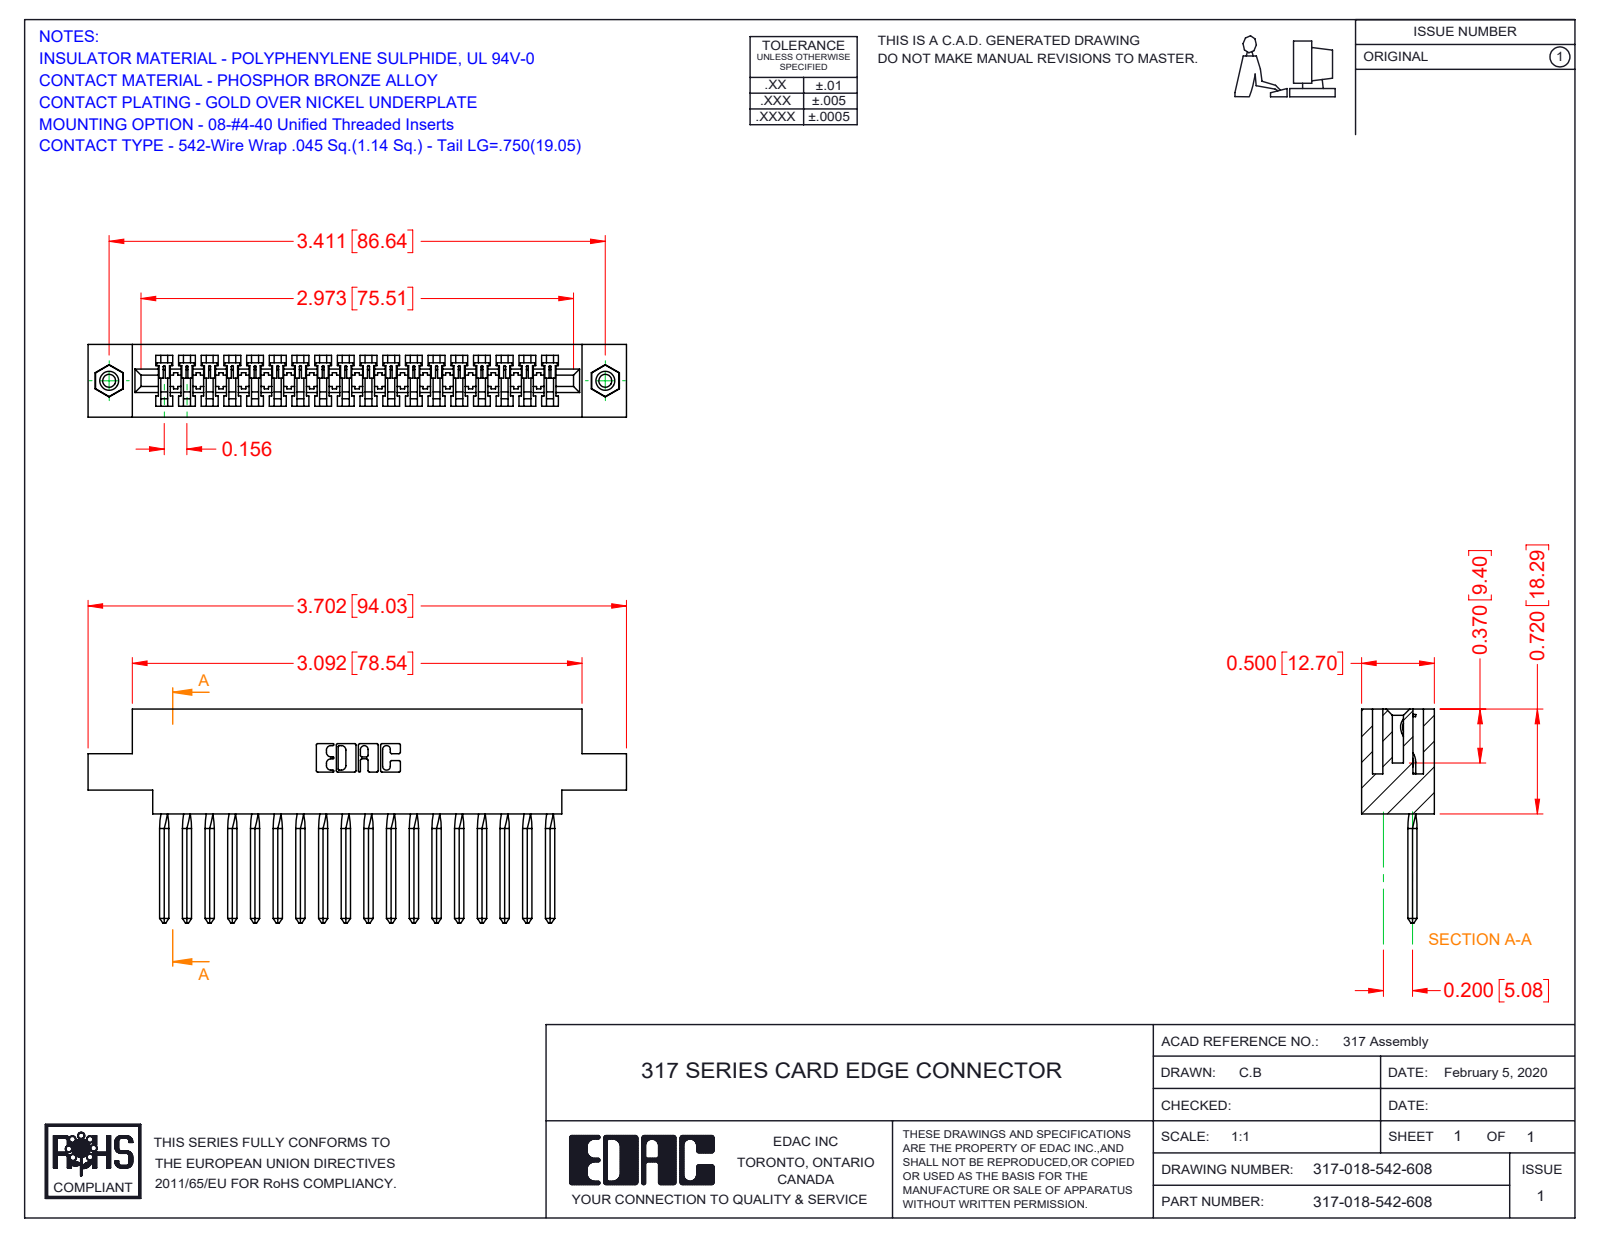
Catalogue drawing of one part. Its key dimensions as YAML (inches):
part_name: "317-018-542-608; 345-250-001_345-250-003-102; 317 Part_.156 Dia - TI; 317-290-003_542"
step_written_by: "SolidWorks 2016 (CONFIG_CONTROL_DESIGN)"
units: inches
bodies: {solids: 21, faces: 1512, planar: 1242, cylindrical: 182, other: 88}
overall_size: [3.702, 1.47, 0.5]
volume: 0.847
surface_area: 25.45
round_holes:
  - {diameter: 0.089, count: 2}
  - {diameter: 0.125, count: 2}
  - {diameter: 0.156, count: 2}
round_bosses_or_shafts:
  - {diameter: 0.155, count: 2}
partial_cylinders:
  - {radius: 0.006, count: 36}
  - {radius: 0.01, count: 22}
  - {radius: 0.007, count: 6}
  - {radius: 0.031, count: 6}
  - {radius: 0.026, count: 3}
  - {radius: 0.074, count: 1}
  - {radius: 0.089, count: 1}
  - {radius: 0.1, count: 1}
face_to_face_distances: [0.5, 0.075, 0.425, 0.11, 0.35, 0.136, 0.72, 0.065, 0.211, 0.289]
hole_center_spacings: [3.411]
